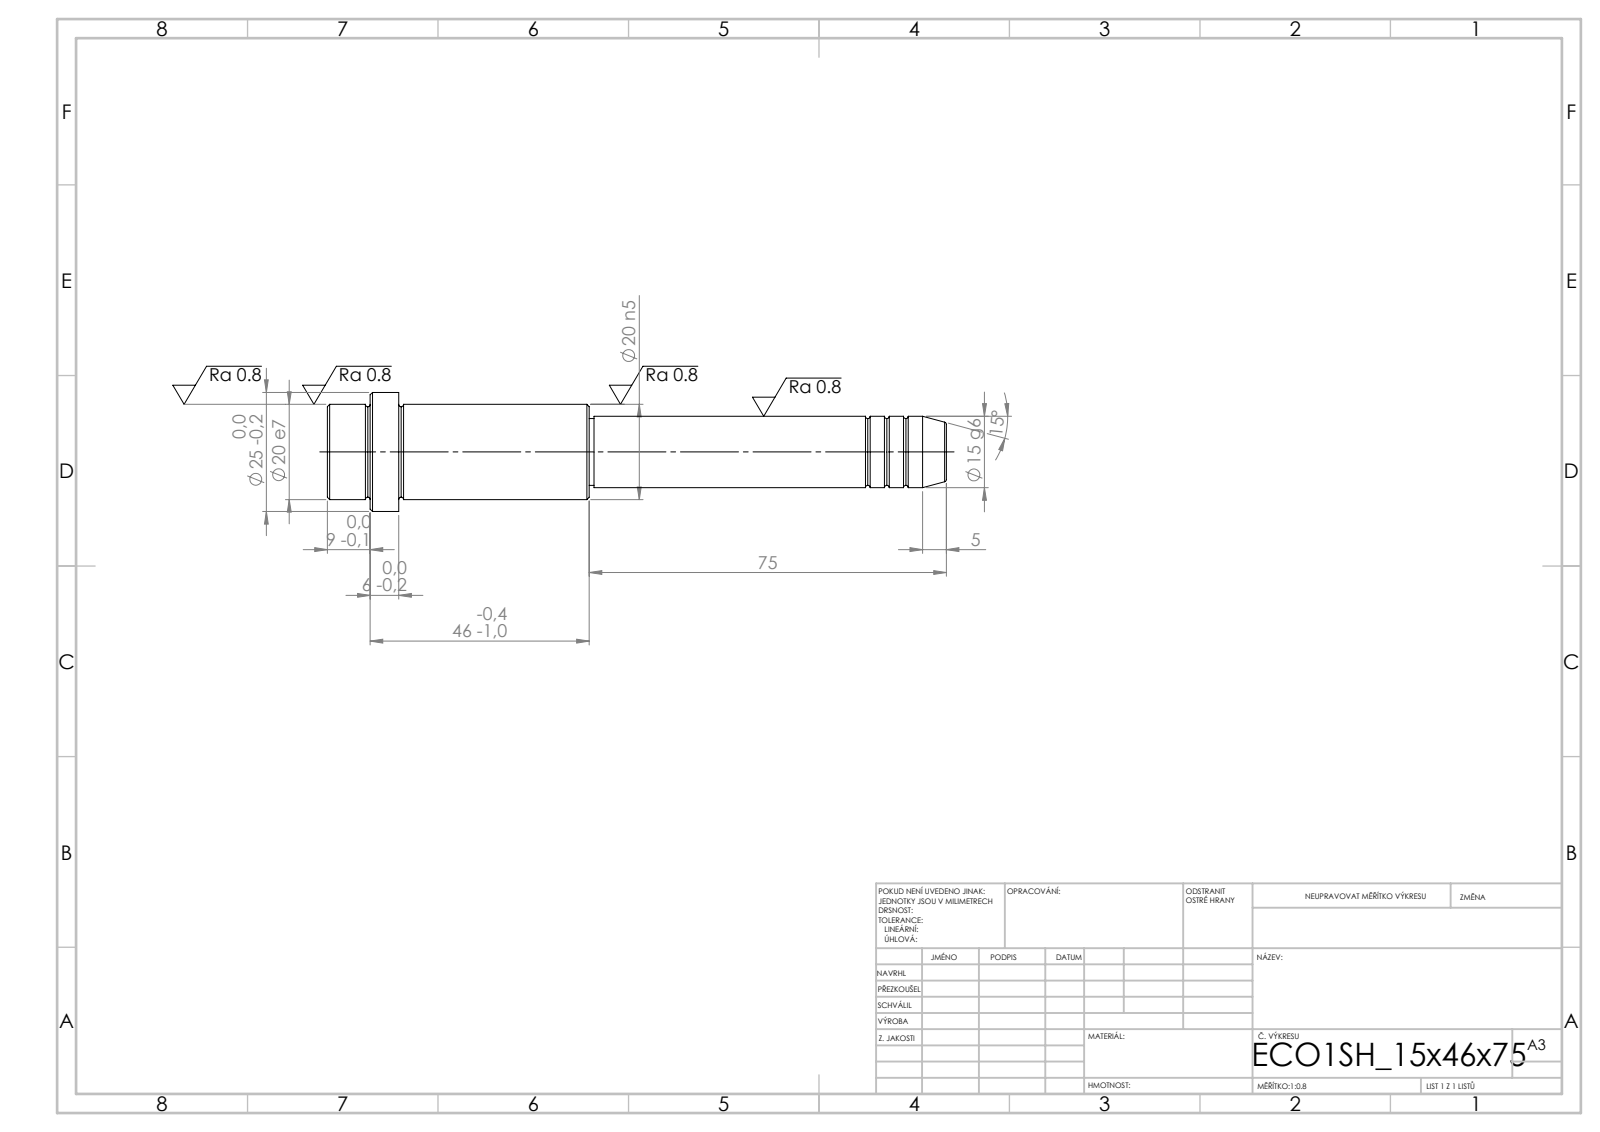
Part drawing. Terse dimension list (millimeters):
written by: SolidWorks 2019 (CONFIG_CONTROL_DESIGN)
unit: mm
bodies: 1 solid, 52 faces (6 planar, 16 cylindrical, 30 other)
size: 130 × 25 × 25
volume: 31 293 mm³; area: 8 109 mm²
bosses: 1× ⌀25, 1× ⌀20, 1× ⌀15, 1× ⌀14
face distances: 15, 6, 9, 40, 46, 55, 75, 115, 121, 130
